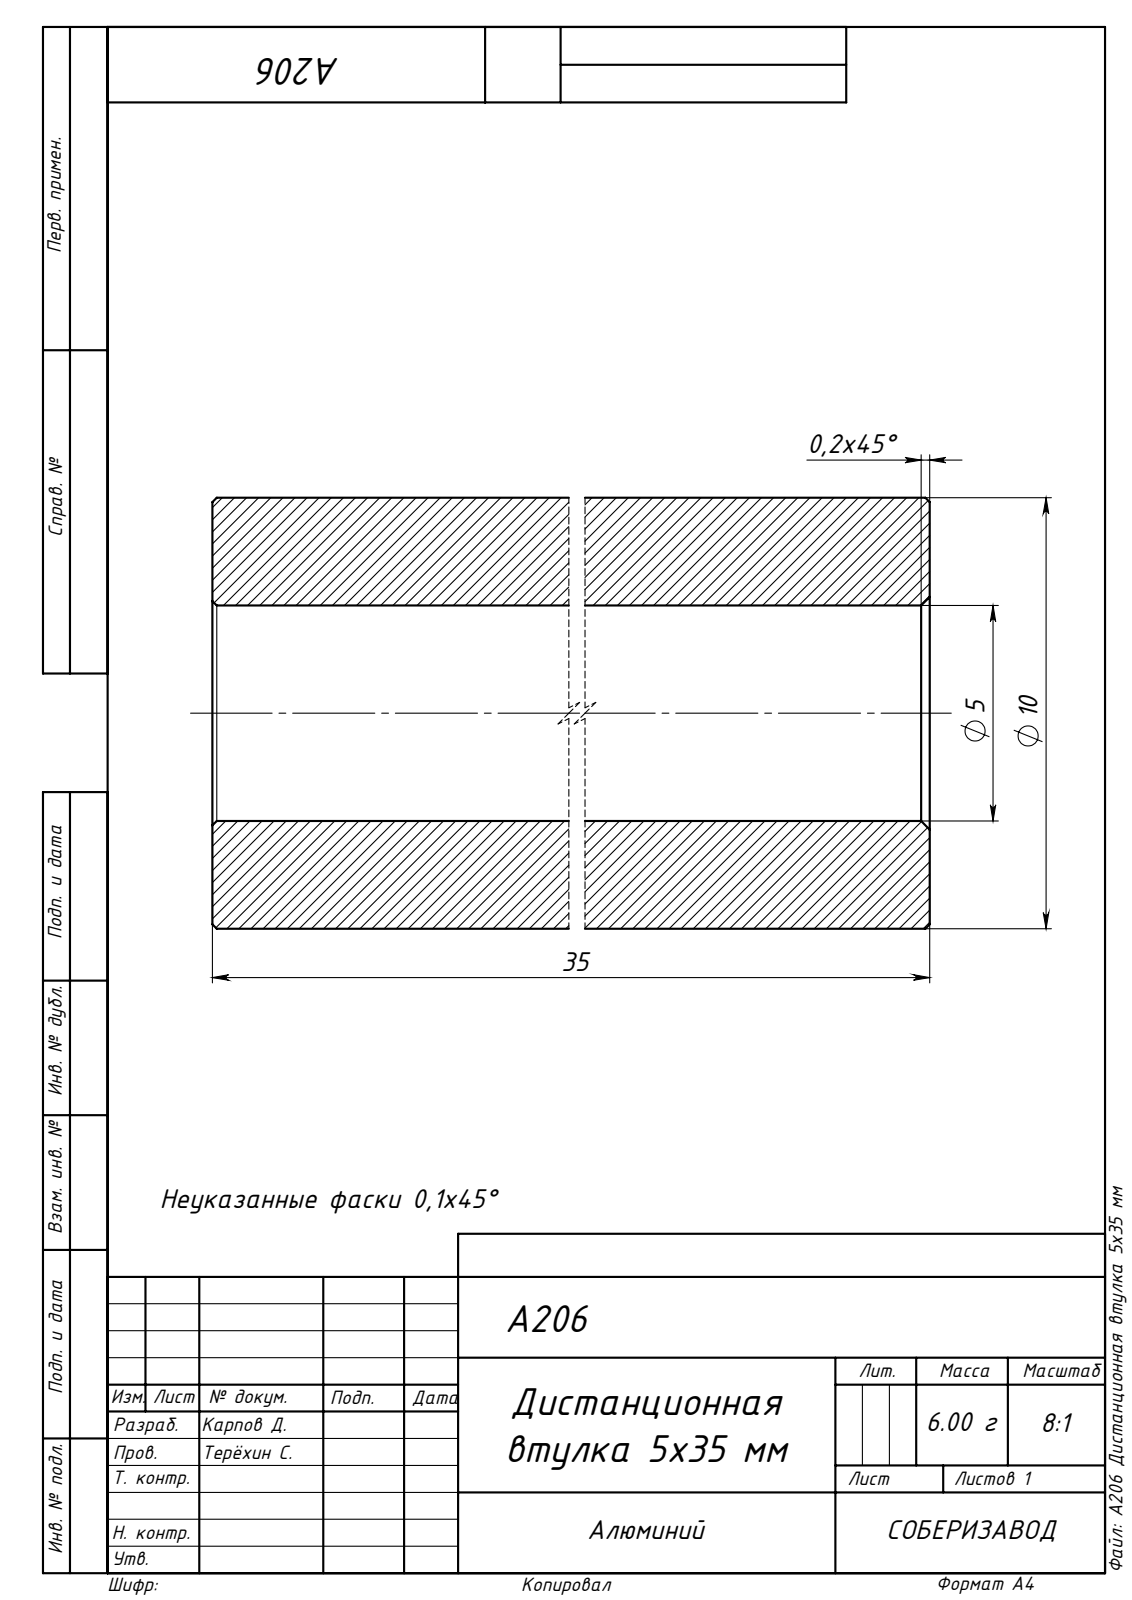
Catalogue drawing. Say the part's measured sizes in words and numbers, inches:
The part is named "A206 Дистанционная втулка 5х35 мм". Its 3-D file was written by "SolidWorks 2020 (AUTOMOTIVE_DESIGN)". It is 1 solid with 14 faces: 2 planar, 4 cylindrical and 8 other. Overall it measures 1.378 by 0.394 by 0.394 inches. Its volume is 0.126 cubic inches and its surface area 2.73 square inches. Round holes: 1 of diameter 0.197. Round bosses or shafts: 1 of diameter 0.394. The main face-to-face distances are 1.378.
